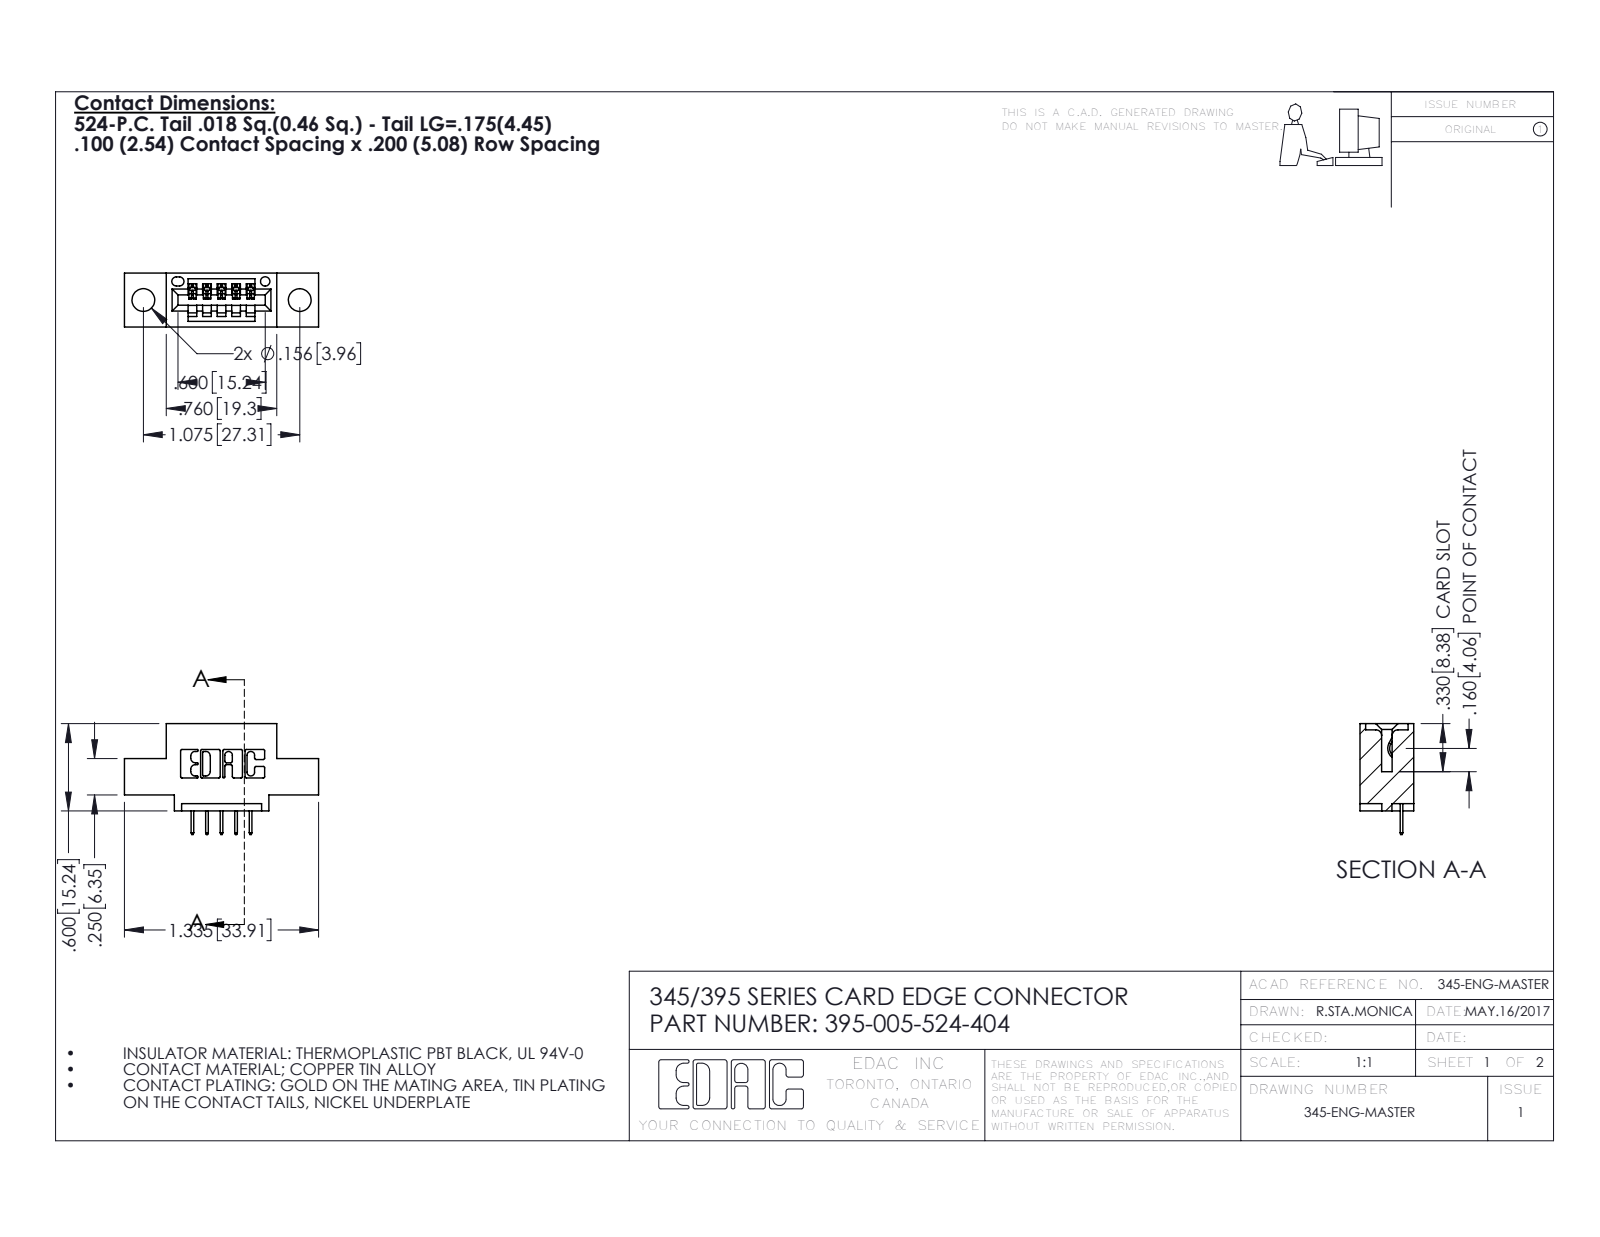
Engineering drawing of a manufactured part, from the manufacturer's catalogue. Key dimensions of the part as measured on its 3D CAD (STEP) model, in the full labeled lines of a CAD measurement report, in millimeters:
Part name (STEP PRODUCT): 345 Part_0.110 Offset - 0.156 Dia-TH; 345-292-001_345-293-124; 395-005-524-404
STEP written by: SolidWorks 2016 (CONFIG_CONTROL_DESIGN)
Units: millimetres
Bodies: 6 solids, 440 faces (314 planar, 126 cylindrical, 0 other)
Overall size (bounding box): 33.9 × 19.4 × 9.4
Volume: 2 740 mm³ · Surface area: 2 961 mm²
Round holes (diameter × count): ⌀4 ×2, ⌀1.6 ×1
Partial cylindrical surfaces — rounded edges, fillets, slot ends (radius × count): R0.3 ×22, R0.2 ×10, R0.2 ×6, R0.8 ×6, R0.7 ×3, R0.8 ×2, R1 ×2, R0.4 ×1
Main face-to-face distances: 9.4, 5.1, 2.5, 1.8, 7.6, 6.4, 0.6, 1.5, 4.1, 14
Hole centre spacings: 6.9, 21.5, 27.3
